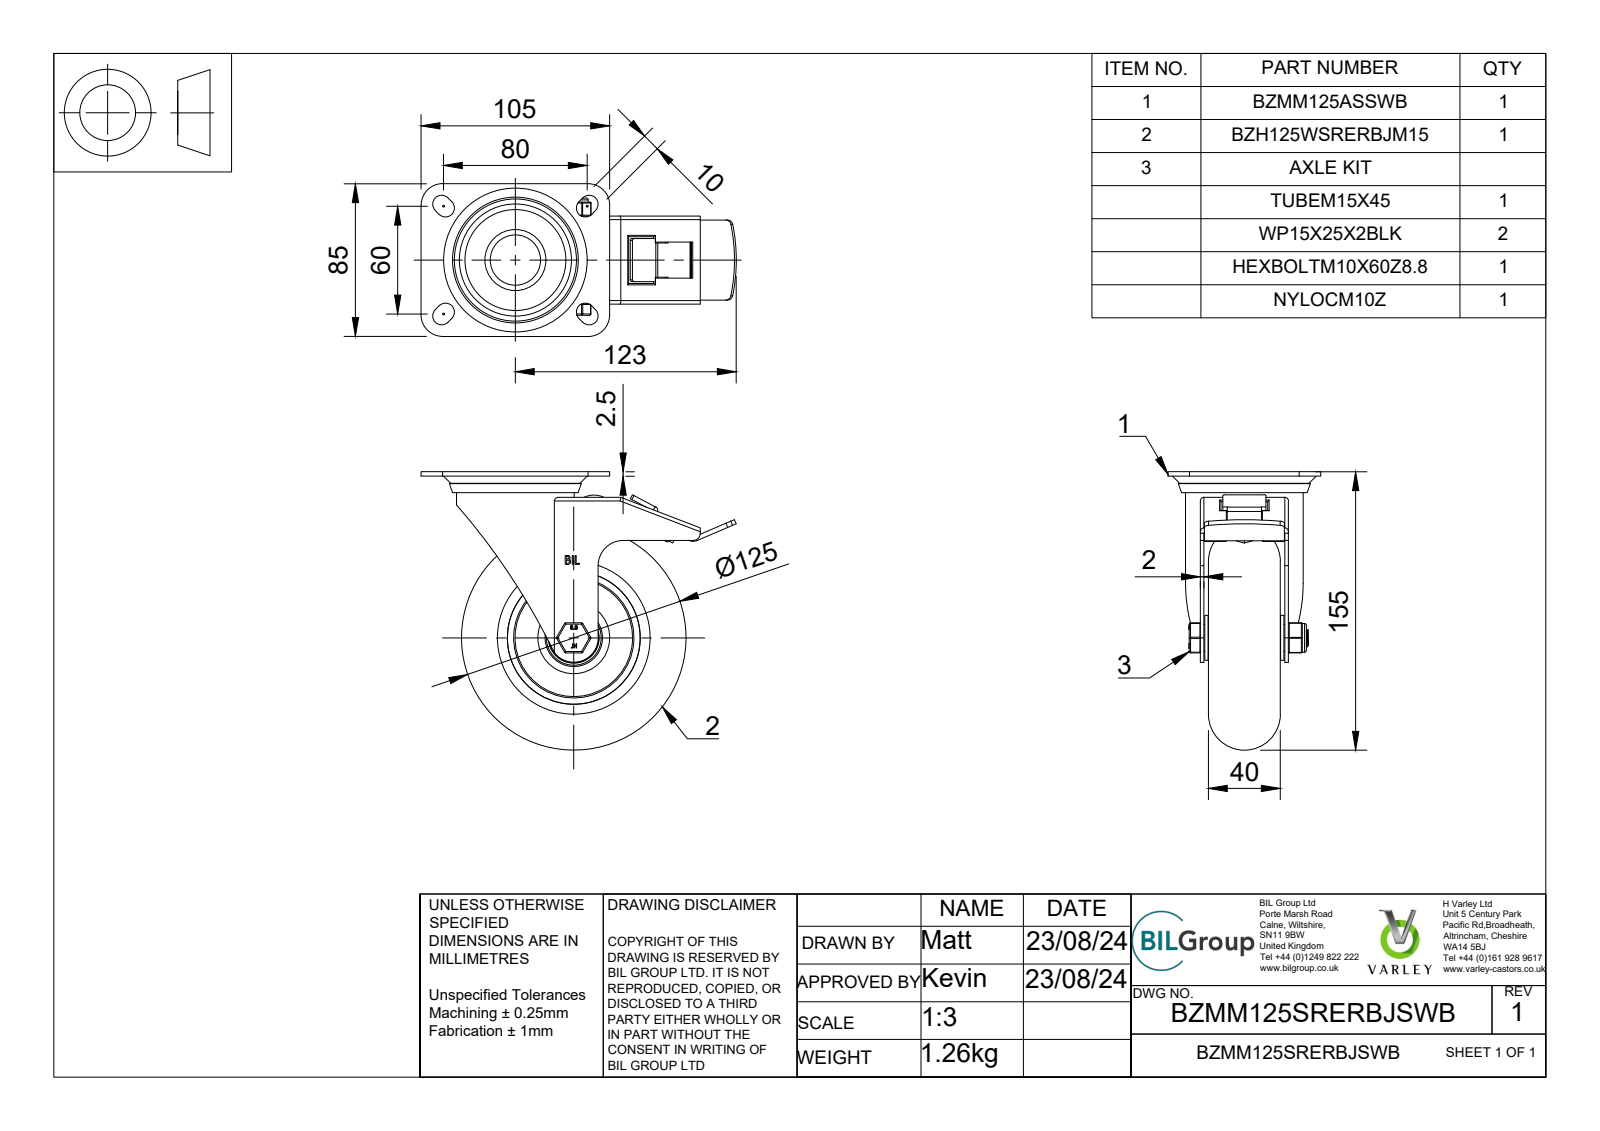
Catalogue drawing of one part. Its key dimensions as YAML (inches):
part_name: "BZMM125SRERBJSWB v3; BZMM125ASSWB v1; ZINC PLATED, PRESSED STEEL TOP PLATE; ZINC PLATED, PRESSED STEEL FORKS (+8 more)"
step_written_by: "Autodesk Translation Framework v13.14.0.145 (AUTOMOTIVE_DESIGN)"
units: inches
bodies: {solids: 45, faces: 1373, planar: 569, cylindrical: 277, other: 527}
overall_size: [6.909, 6.102, 3.346]
volume: 26.91
surface_area: 258.6
round_holes:
  - {diameter: 0.236, count: 2}
  - {diameter: 1.102, count: 2}
  - {diameter: 0.394, count: 1}
  - {diameter: 0.402, count: 1}
  - {diameter: 0.472, count: 1}
  - {diameter: 0.591, count: 1}
  - {diameter: 0.62, count: 1}
  - {diameter: 0.807, count: 1}
  - {diameter: 1.024, count: 1}
  - {diameter: 1.055, count: 1}
  - {diameter: 1.11, count: 1}
  - {diameter: 1.26, count: 1}
round_bosses_or_shafts:
  - {diameter: 2.579, count: 1}
  - {diameter: 1.575, count: 1}
  - {diameter: 1.339, count: 1}
  - {diameter: 0.984, count: 1}
  - {diameter: 0.846, count: 1}
  - {diameter: 0.787, count: 1}
  - {diameter: 0.748, count: 1}
  - {diameter: 0.63, count: 1}
partial_cylinders:
  - {radius: 0.02, count: 18}
  - {radius: 0.03, count: 16}
  - {radius: 0.059, count: 12}
  - {radius: 0.197, count: 9}
  - {radius: 0.039, count: 8}
  - {radius: 0.079, count: 6}
  - {radius: 0.118, count: 4}
  - {radius: 0.472, count: 4}
face_to_face_distances: [0.079, 0.098, 0.177, 1.752, 1.85, 1.673, 0.354, 0.453, 0.197, 0.719]
hole_center_spacings: [1.722]
